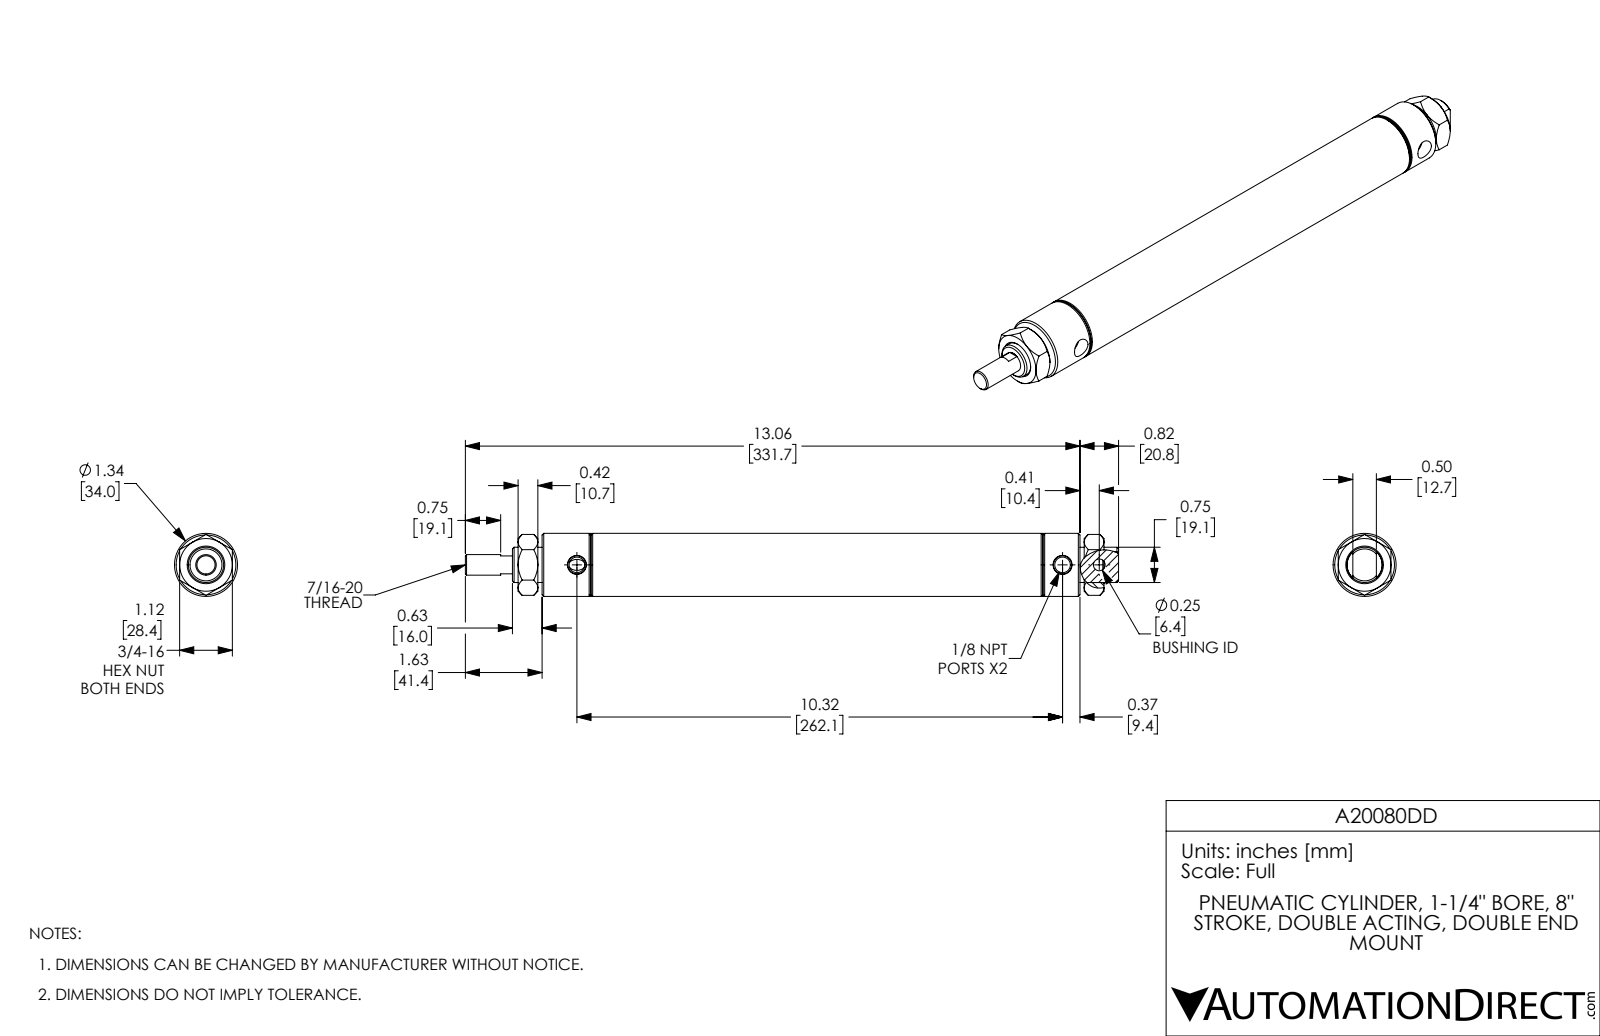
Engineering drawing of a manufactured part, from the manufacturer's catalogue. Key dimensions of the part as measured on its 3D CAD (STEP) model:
Part name (STEP PRODUCT): A20080DD; A20080DD_Mounting Nut_D-3556; A20080DD-Rod; A20080DD-MainBody
STEP written by: SolidWorks 2017 (AUTOMOTIVE_DESIGN)
Units: inches
Bodies: 4 solids, 138 faces (44 planar, 36 cylindrical, 58 other)
Overall size (bounding box): 13.88 × 1.34 × 1.34
Volume: 8.604 in³ · Surface area: 121.4 in²
Round holes (diameter × count): ⌀0.332 ×2, ⌀0.251 ×1, ⌀0.437 ×1, ⌀0.75 ×1, ⌀1.25 ×1
Round bosses / shafts (diameter × count): ⌀1.34 ×1, ⌀0.747 ×1
Main face-to-face distances: 1.465, 9.965, 0.5, 1.12, 8.5, 8, 0.31, 0.42, 12.03, 1.965
Hole centre spacings: 0.78, 10.32, 11.1
